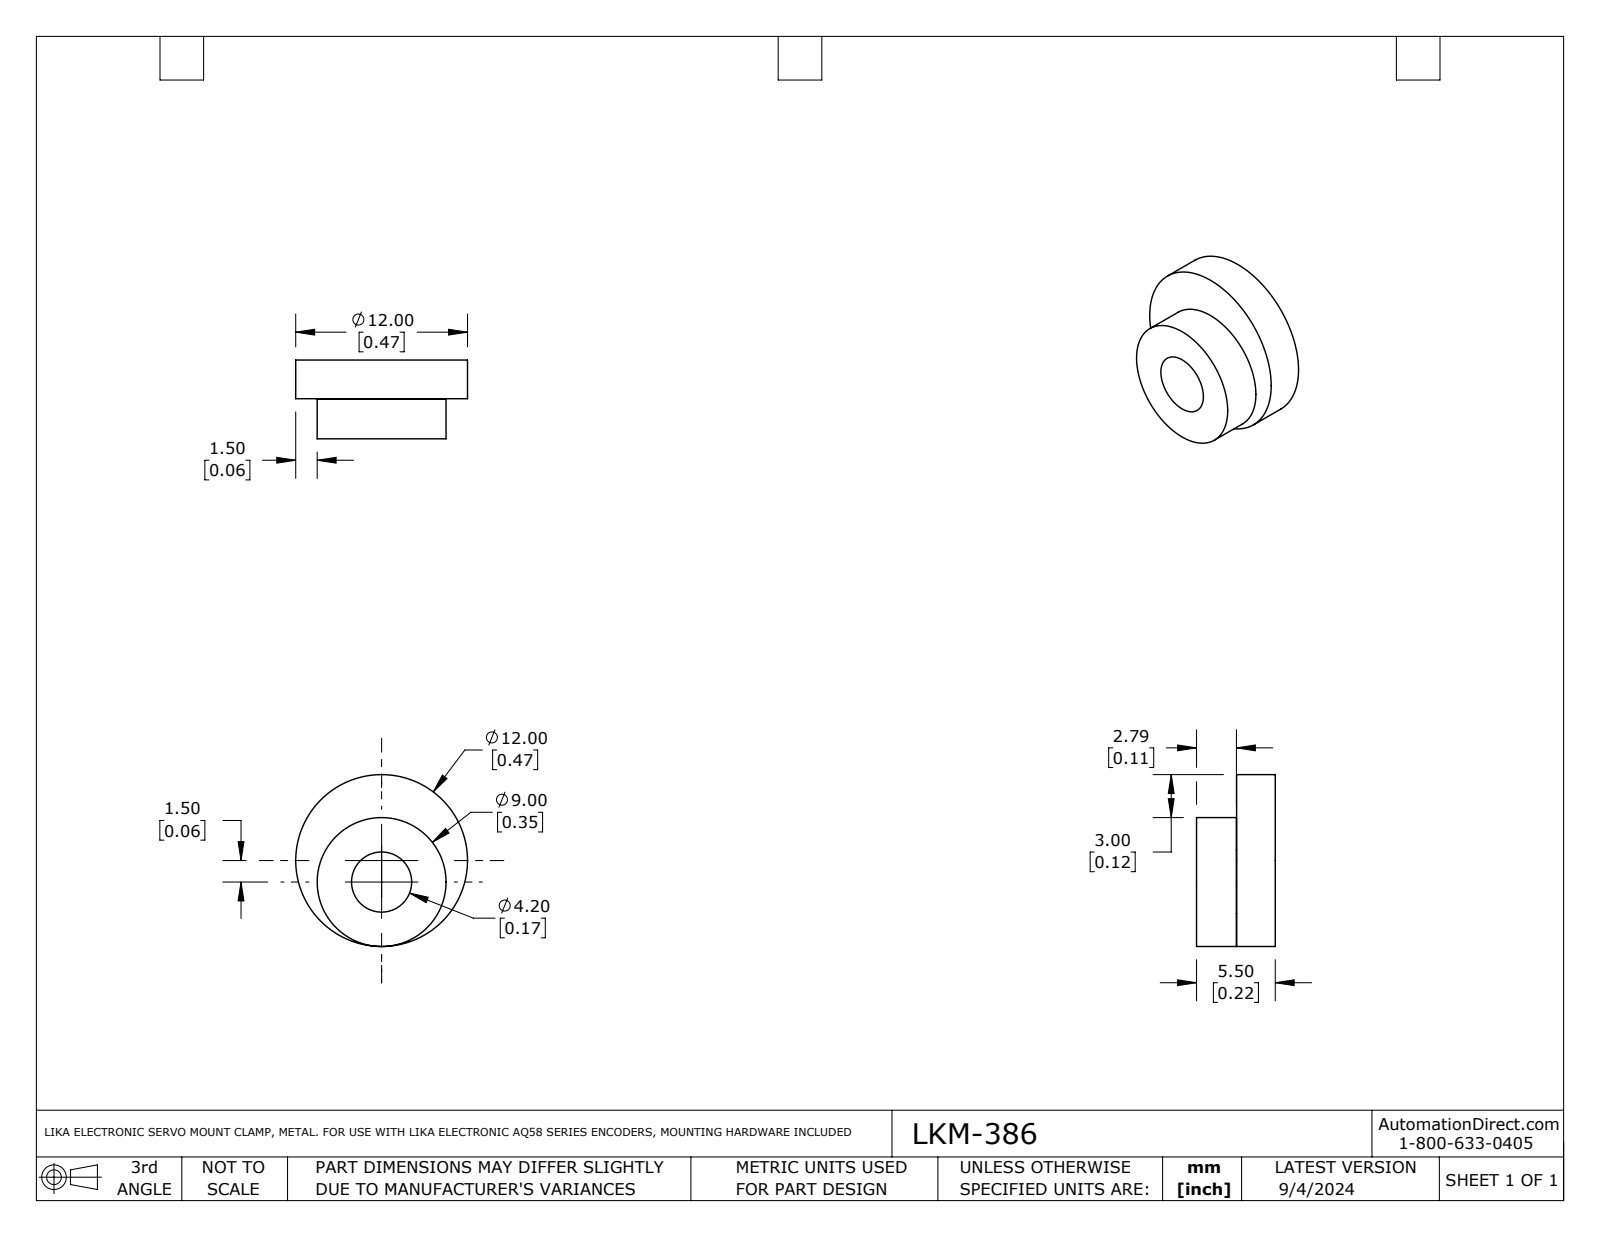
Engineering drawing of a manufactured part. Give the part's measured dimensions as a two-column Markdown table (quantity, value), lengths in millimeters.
| quantity | value |
| --- | --- |
| part name | LKM-386 |
| STEP written by | SolidWorks 2021 (AUTOMOTIVE_DESIGN) |
| units | millimeters |
| bodies | 1 solid, 12 faces (4 planar, 8 cylindrical, 0 other) |
| overall size | 12 × 12 × 5.5 |
| volume | 410 mm³ |
| surface area | 548 mm² |
| round holes (diameter × count) | 4.2 × 1 |
| round bosses / shafts (diameter × count) | 12 × 1, 9 × 1, 4.4 × 1 |
| main face-to-face distances | 2.7, 5.5, 2.8, 2.7, 2.8 |
